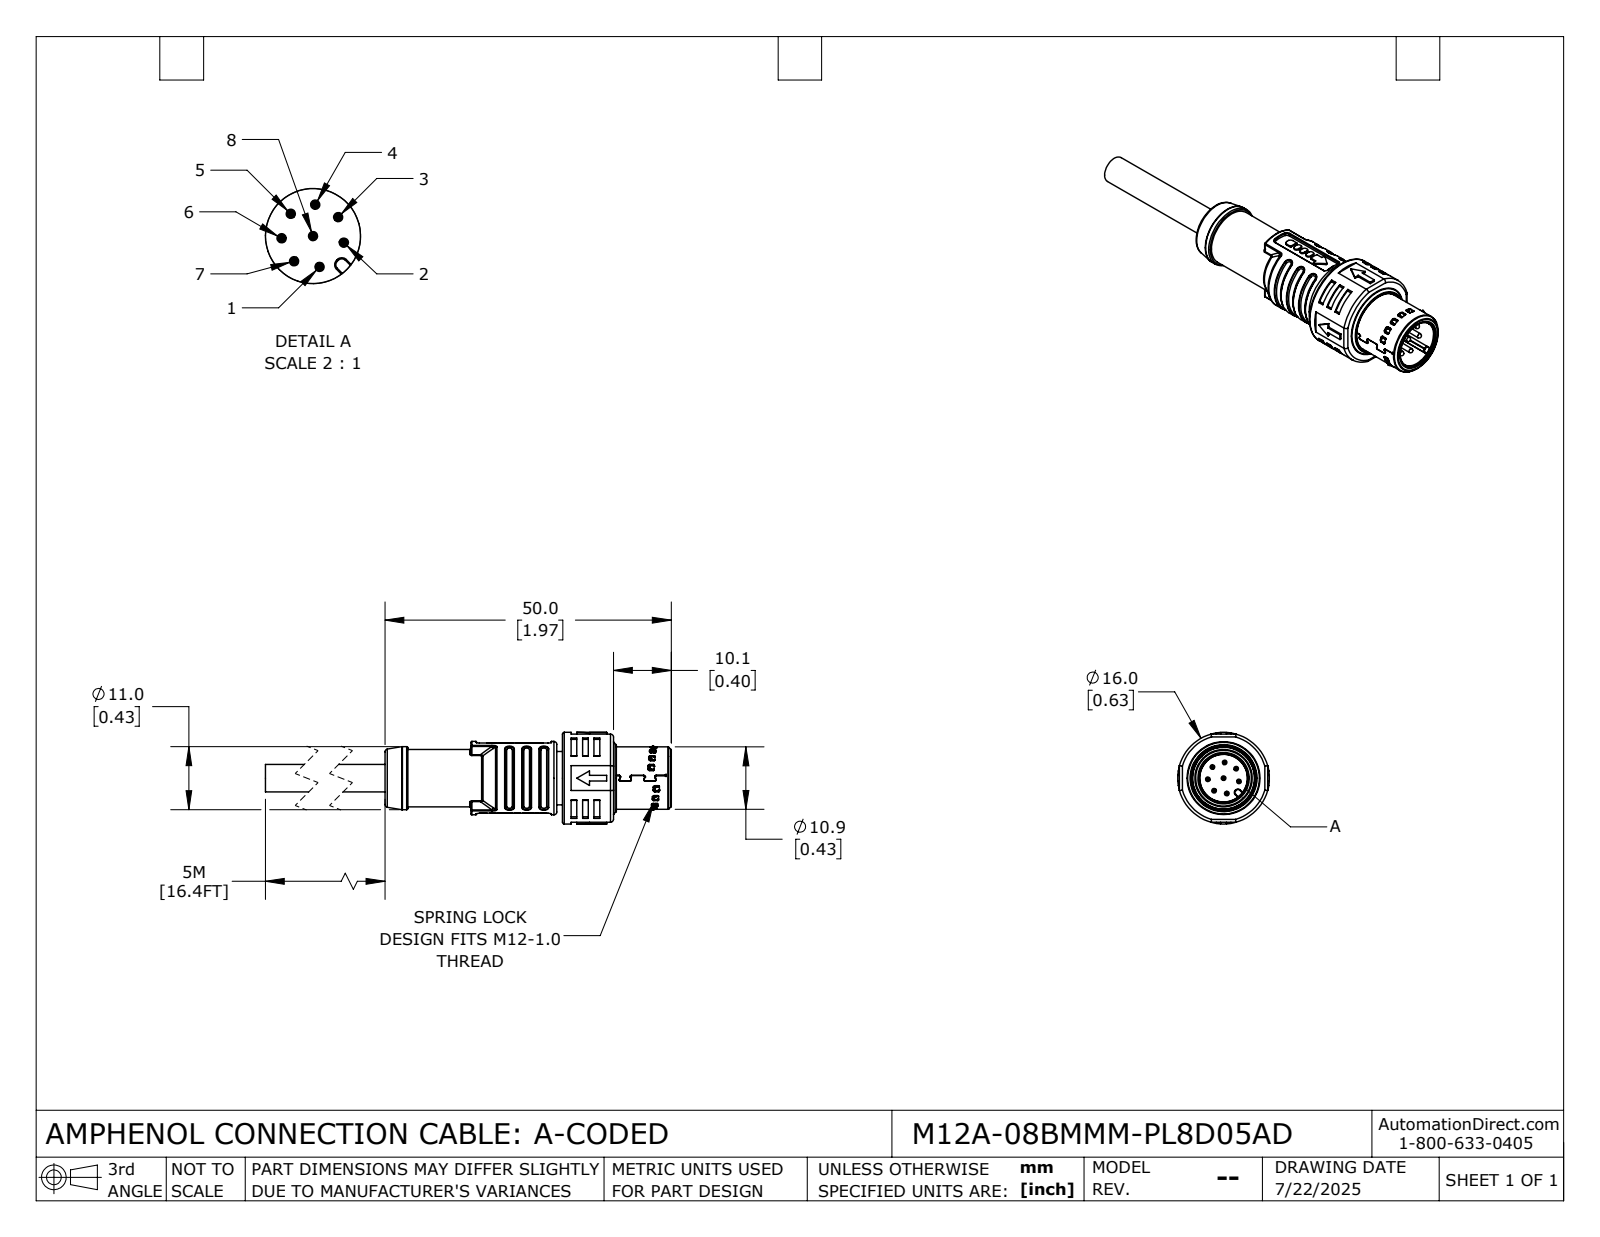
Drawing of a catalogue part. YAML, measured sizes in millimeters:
part_name: "M12A-08BMMM-PL8D05AD"
step_written_by: "SolidWorks 2024 (CONFIG_CONTROL_DESIGN)"
units: millimeters
bodies: {solids: 1, faces: 2027, planar: 880, cylindrical: 644, other: 503}
overall_size: [75, 16, 16]
volume: 5223
surface_area: 5723
round_holes:
  - {diameter: 8.3, count: 1}
  - {diameter: 9, count: 1}
  - {diameter: 10.15, count: 1}
  - {diameter: 10.5, count: 1}
  - {diameter: 10.9, count: 1}
  - {diameter: 11.5, count: 1}
  - {diameter: 11.8, count: 1}
  - {diameter: 14.2, count: 1}
round_bosses_or_shafts:
  - {diameter: 0.8, count: 8}
  - {diameter: 16, count: 1}
  - {diameter: 14.1, count: 1}
  - {diameter: 12.8, count: 1}
  - {diameter: 12.4, count: 1}
  - {diameter: 11, count: 1}
  - {diameter: 10.45, count: 1}
  - {diameter: 10.4, count: 1}
partial_cylinders:
  - {radius: 0.2, count: 114}
  - {radius: 0.25, count: 66}
  - {radius: 0.3, count: 64}
  - {radius: 0.15, count: 44}
  - {radius: 0.5, count: 38}
  - {radius: 0.13, count: 12}
  - {radius: 0.7, count: 11}
  - {radius: 0.1, count: 10}
face_to_face_distances: [1, 10.1, 8.6, 8.9, 2.5, 1.5, 1.2, 32.5, 15.4, 41.1]
